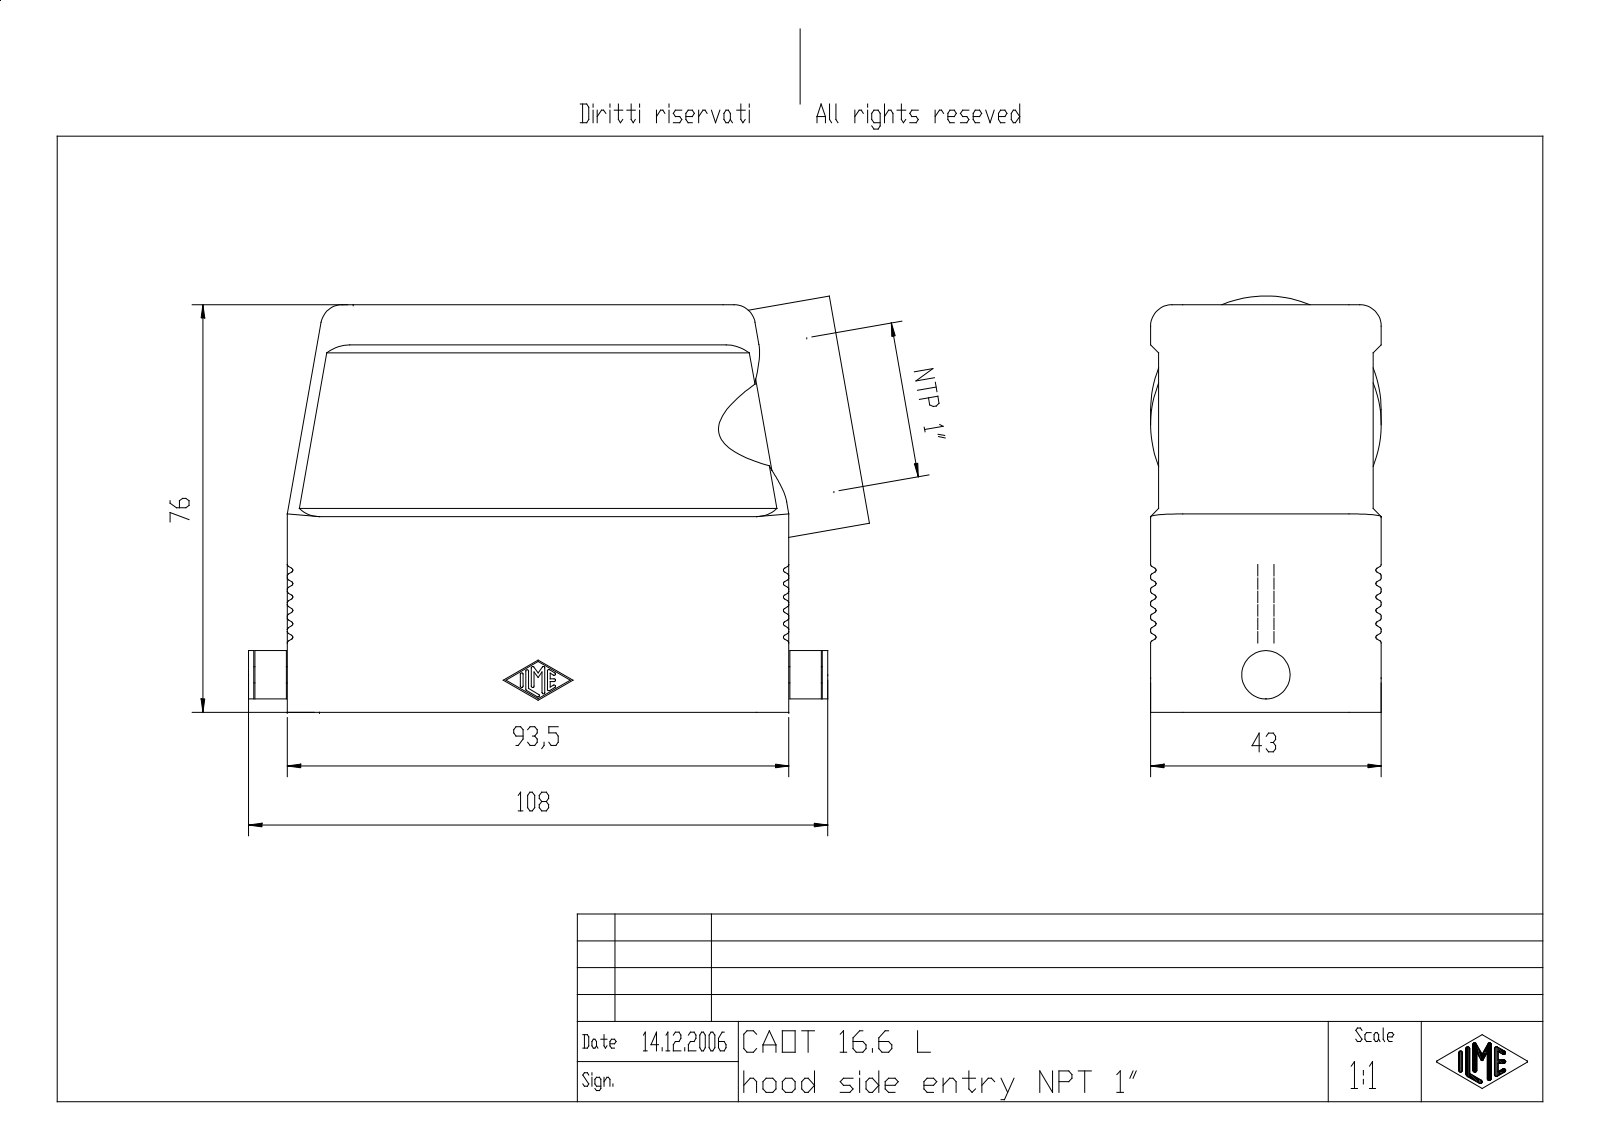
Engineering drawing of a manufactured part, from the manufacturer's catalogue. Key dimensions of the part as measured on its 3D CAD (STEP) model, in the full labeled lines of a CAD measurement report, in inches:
Part name (STEP PRODUCT): MSBO14359
STEP written by: Creo Elements/Direct Modeling 18.0B 02-Dec-2011 (C) Parametric Technology GmbH (AUTOMOTIVE_DESIGN)
Units: inches
Bodies: 1 solid, 661 faces (234 planar, 264 cylindrical, 163 other)
Overall size (bounding box): 4.558 × 3.056 × 1.693
Volume: 4.813 in³ · Surface area: 76.31 in²
Round holes (diameter × count): ⌀0.097 ×4, ⌀0.122 ×4
Round bosses / shafts (diameter × count): ⌀1.693 ×1, ⌀0.354 ×1, ⌀0.118 ×1
Partial cylindrical surfaces — rounded edges, fillets, slot ends (radius × count): R0.016 ×96, R0.01 ×14, R0.236 ×10, R0.059 ×4, R0.118 ×4, R0.157 ×4, R0.197 ×4
Main face-to-face distances: 0.059, 0.118, 1.575, 1.457, 1.516, 1.634, 1.693, 0.325, 3.12, 0.443
Hole centre spacings: 1.063, 3.051, 3.231
